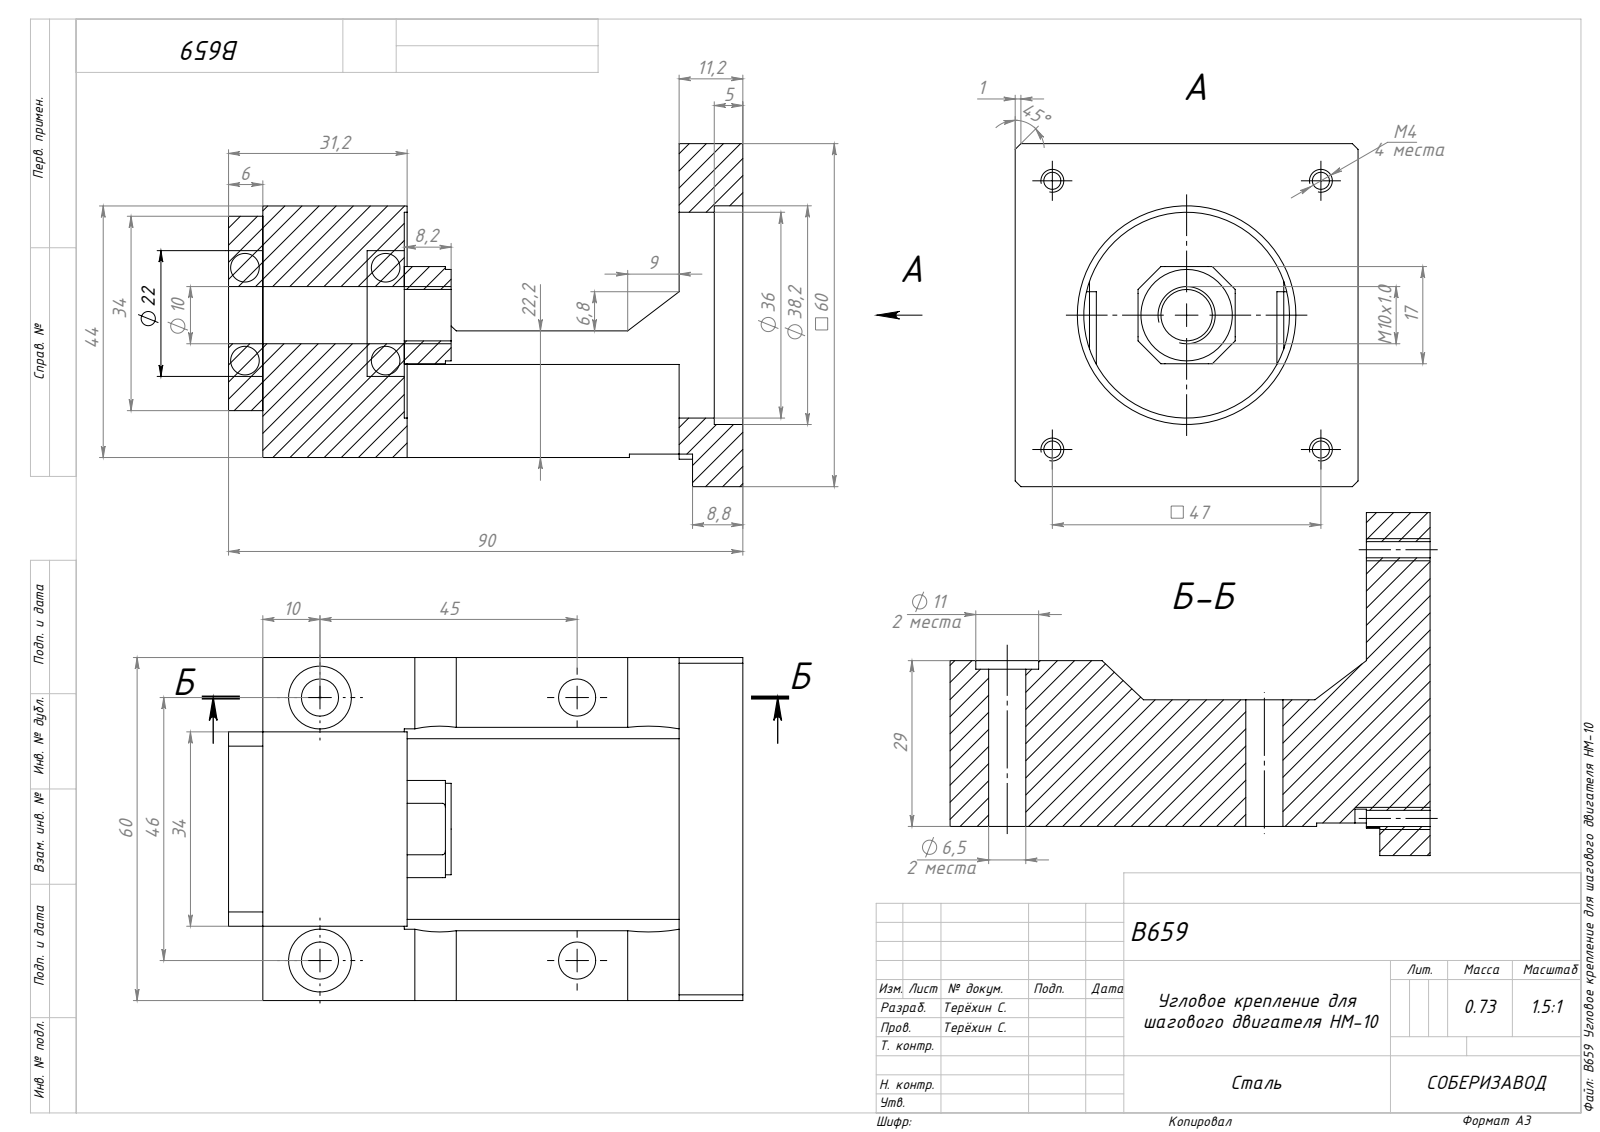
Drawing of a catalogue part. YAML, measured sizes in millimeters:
part_name: "B659 Угловое крепление для шагового двигателя HM-10_00; B659 Угловое крепление для шагового двигателя HM-10"
step_written_by: "SolidWorks 2026 (CONFIG_CONTROL_DESIGN)"
units: millimeters
bodies: {solids: 4, faces: 127, planar: 67, cylindrical: 60, other: 0}
overall_size: [90, 60, 60]
volume: 117030
surface_area: 34940
round_holes:
  - {diameter: 3, count: 4}
  - {diameter: 6.5, count: 4}
  - {diameter: 7.6, count: 4}
  - {diameter: 3.4, count: 2}
  - {diameter: 11, count: 2}
  - {diameter: 9, count: 1}
  - {diameter: 10, count: 1}
  - {diameter: 36, count: 1}
  - {diameter: 38.25, count: 1}
round_bosses_or_shafts:
  - {diameter: 16, count: 1}
partial_cylinders:
  - {radius: 0.5, count: 8}
face_to_face_distances: [60, 14.2, 45.8, 32.8, 13, 47, 1.2, 84, 31.6, 11.15]
hole_center_spacings: [37.64, 15.56, 17.68, 25, 33.23, 47, 50.91, 35.36]
